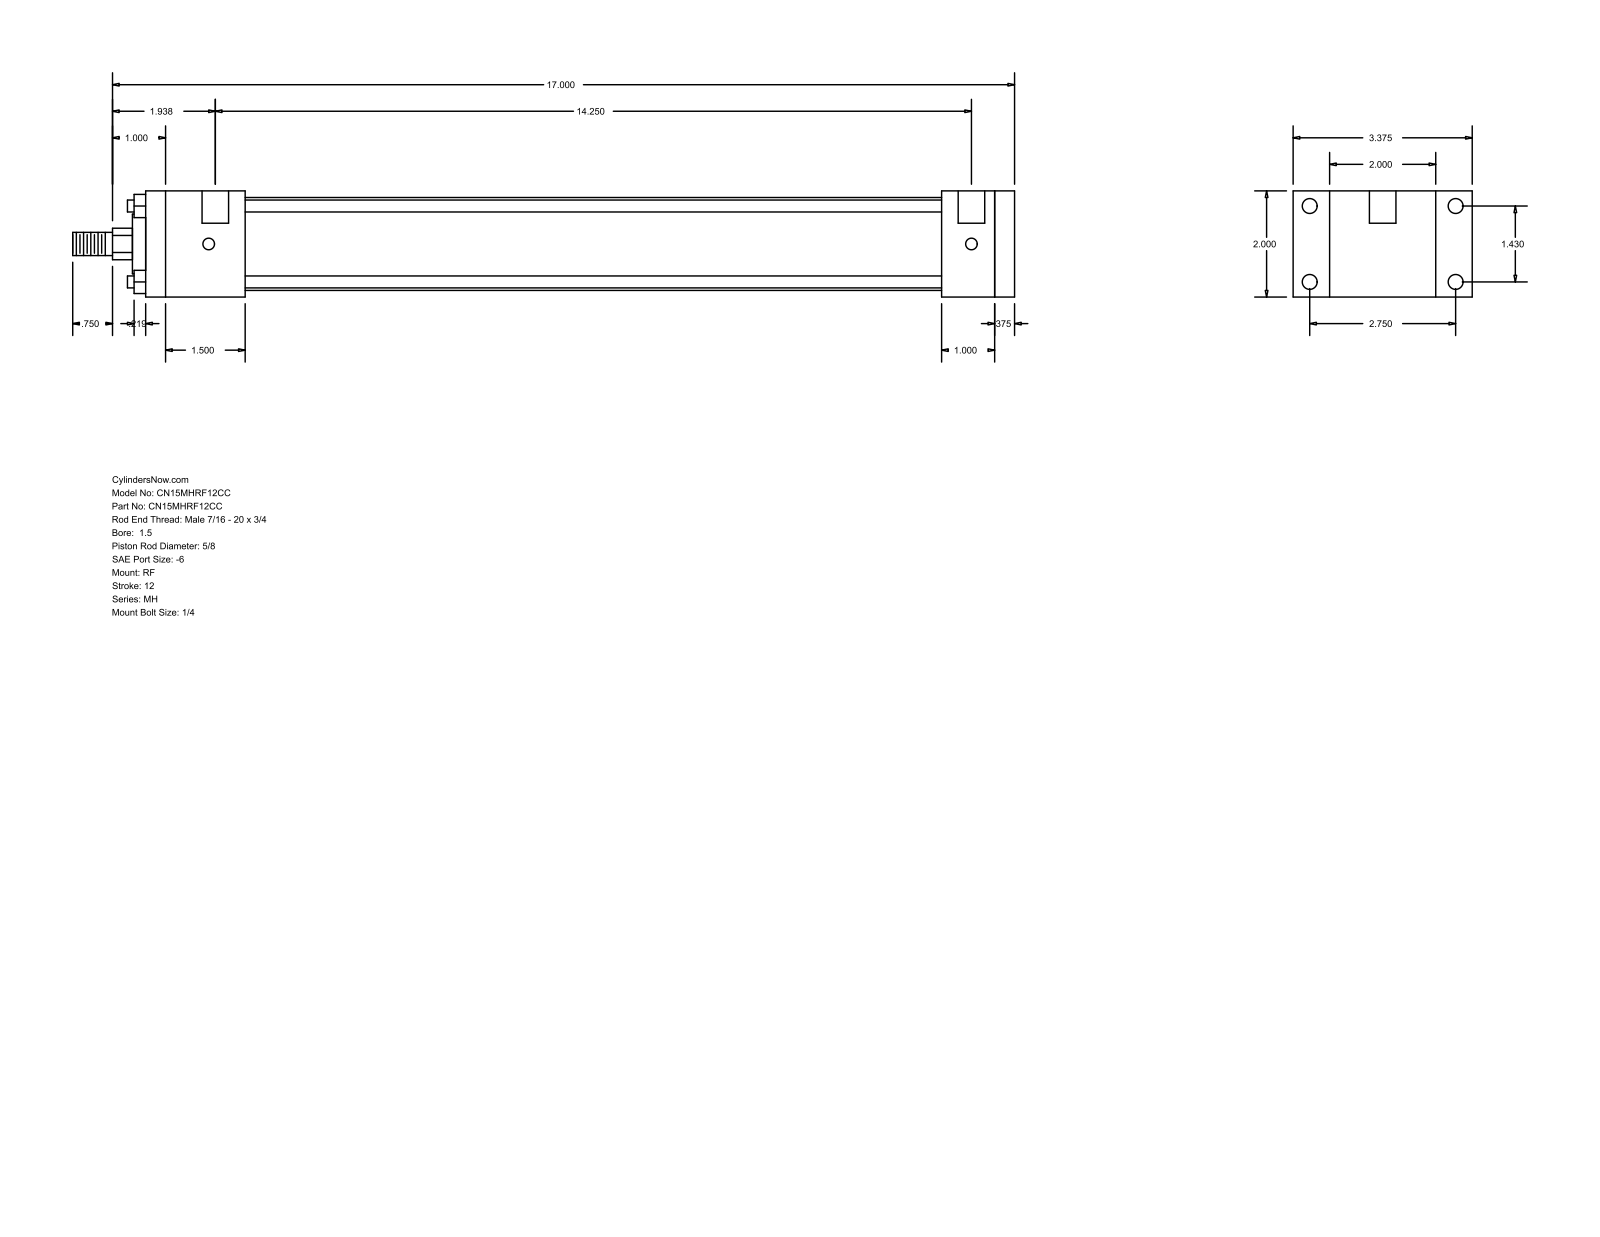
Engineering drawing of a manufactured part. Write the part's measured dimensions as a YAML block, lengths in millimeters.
part_name: "MH_RF__0150_0.625"
step_written_by: "GSSL Pune (CONFIG_CONTROL_DESIGN)"
units: millimeters
bodies: {solids: 0, faces: 92, planar: 64, cylindrical: 28, other: 0}
overall_size: [450.85, 85.72, 50.8]
round_holes:
  - {diameter: 5.56, count: 4}
  - {diameter: 7.14, count: 4}
  - {diameter: 12.7, count: 2}
round_bosses_or_shafts:
  - {diameter: 5.71, count: 4}
  - {diameter: 44.45, count: 1}
  - {diameter: 28.57, count: 1}
  - {diameter: 15.88, count: 1}
  - {diameter: 11.11, count: 1}
partial_cylinders:
  - {radius: 7.54, count: 1}
face_to_face_distances: [50.8, 9.53, 415.92, 406.39, 17.46, 68.26, 381, 25.39, 34.92, 47.62]
hole_center_spacings: [36.32, 69.84, 78.72, 365.12, 3.17, 361.95]
